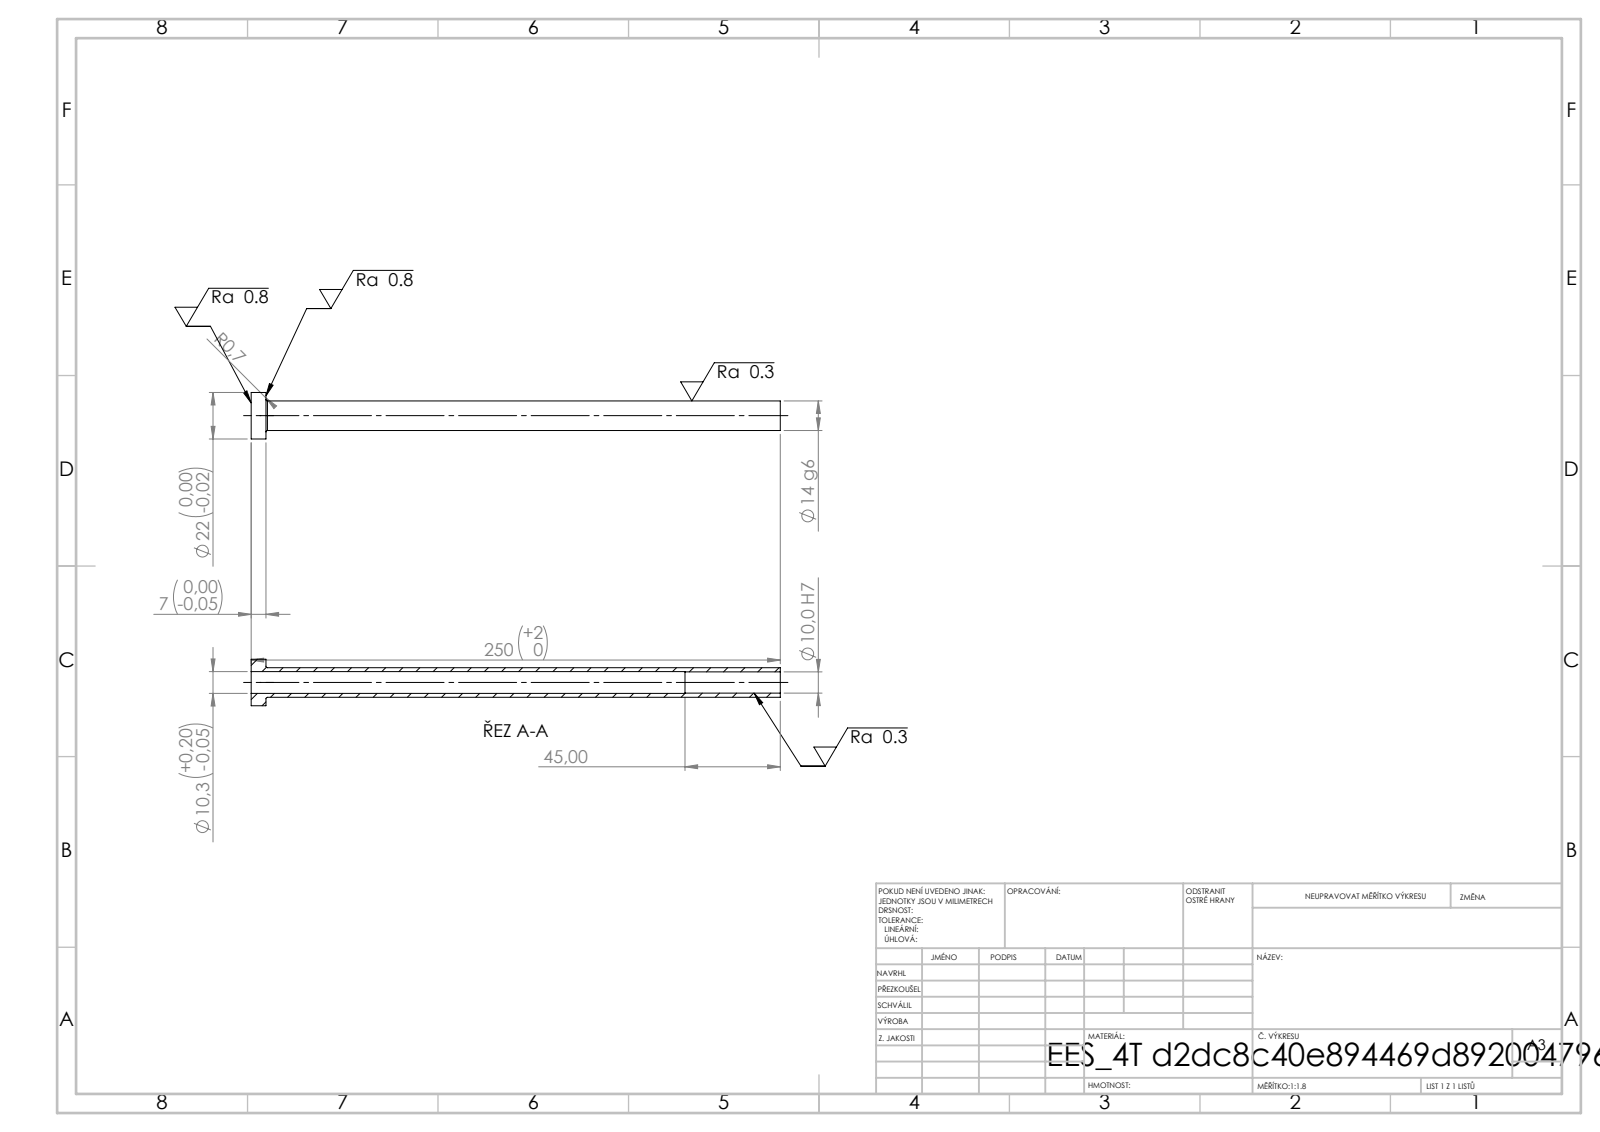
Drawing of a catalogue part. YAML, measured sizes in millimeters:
step_written_by: "SolidWorks 2019 (CONFIG_CONTROL_DESIGN)"
units: millimeters
bodies: {solids: 1, faces: 14, planar: 4, cylindrical: 8, other: 2}
overall_size: [250, 22, 22]
volume: 19457
surface_area: 19809
round_holes:
  - {diameter: 10, count: 1}
  - {diameter: 10.3, count: 1}
round_bosses_or_shafts:
  - {diameter: 22, count: 1}
  - {diameter: 14, count: 1}
face_to_face_distances: [7, 250, 243, 205, 198, 45]
